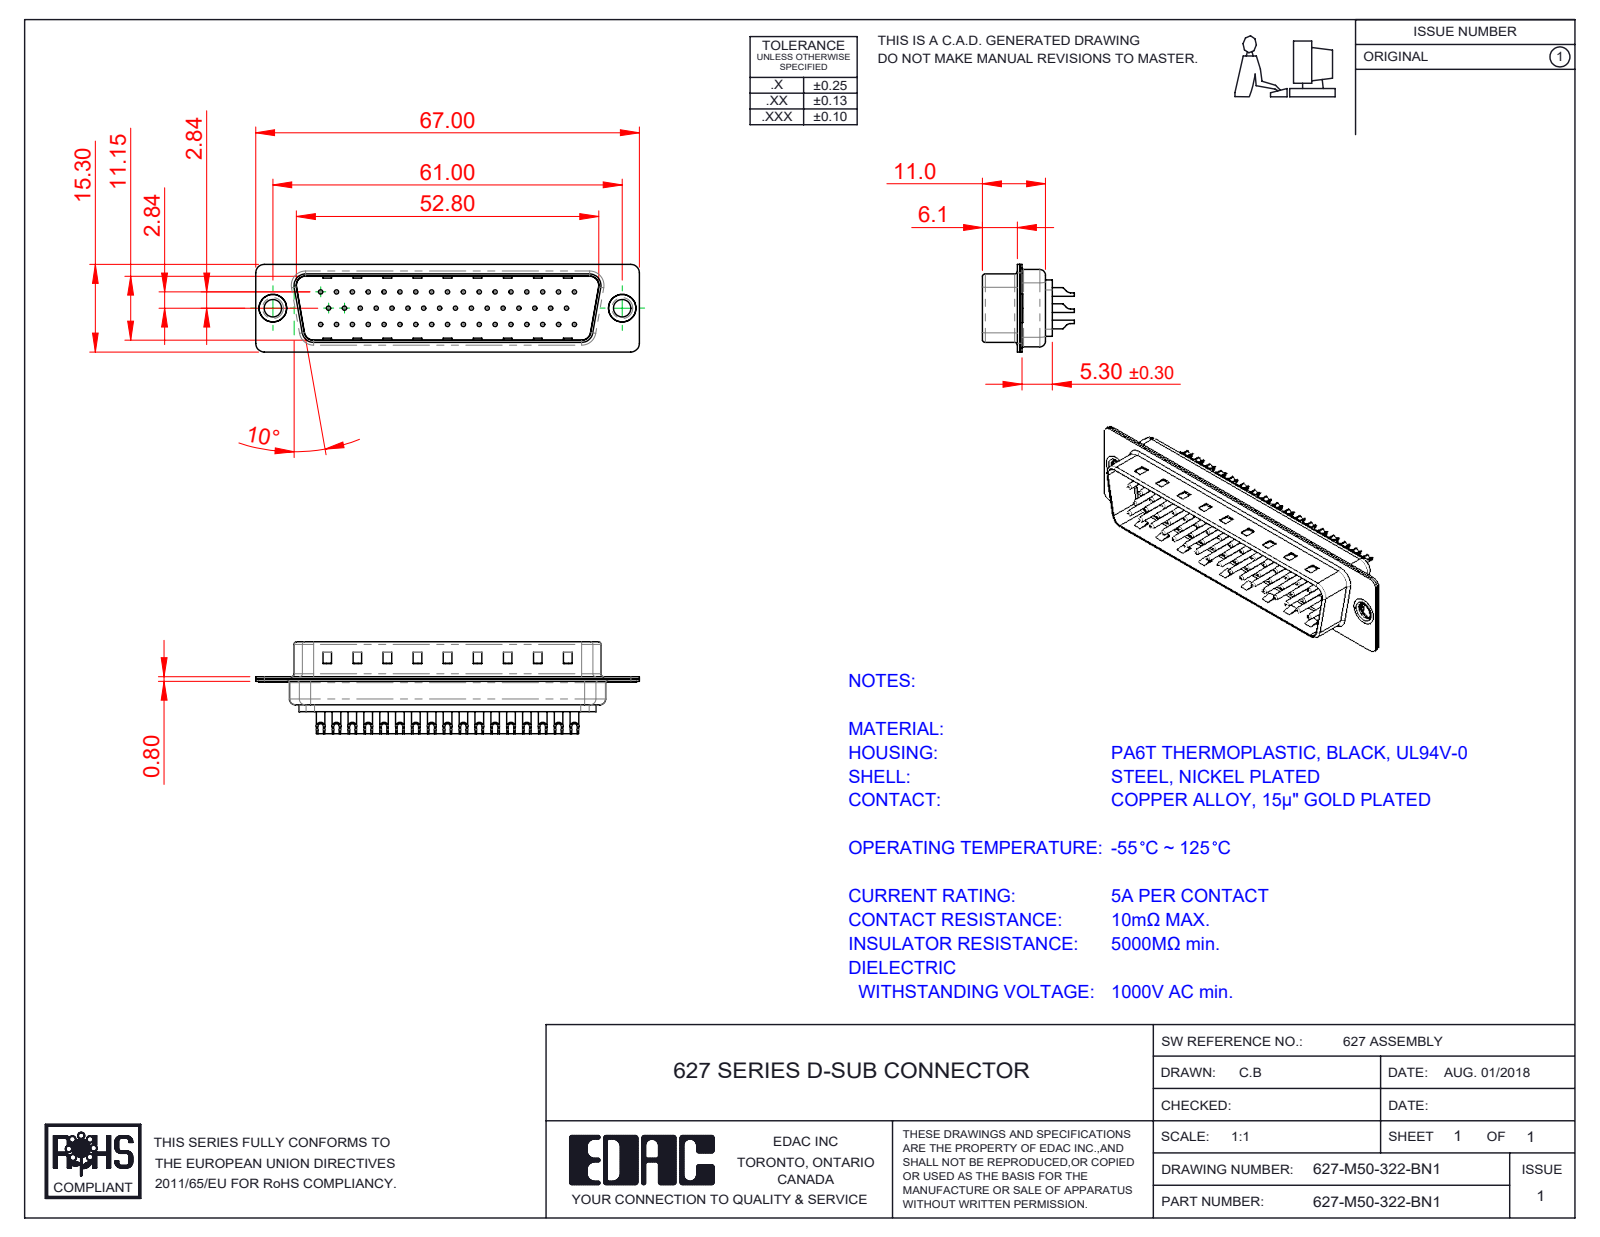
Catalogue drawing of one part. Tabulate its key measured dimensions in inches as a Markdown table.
| quantity | value |
| --- | --- |
| part name | 627M Contact Row 1_22; 627M Shell Front_50 Contacts; 627-M50-322-BN1; 627M Contact Row 2_22L (+4 more) |
| STEP written by | SolidWorks 2020 (CONFIG_CONTROL_DESIGN) |
| units | inches |
| bodies | 55 solids, 2236 faces (653 planar, 925 cylindrical, 658 other) |
| overall size | 2.638 × 0.632 × 0.602 |
| volume | 0.278 in³ |
| surface area | 17.08 in² |
| round holes (diameter × count) | 0.03 × 50, 0.039 × 50, 0.063 × 50, 0.079 × 50, 0.12 × 2, 0.157 × 2, 0.189 × 2 |
| round bosses / shafts (diameter × count) | 0.059 × 50, 0.197 × 2, 0.193 × 2, 0.14 × 2 |
| partial cylindrical surfaces (radius × count) | 0.059 × 16, 0.079 × 12, 0.02 × 8, 0.063 × 8, 0.039 × 7, 0.01 × 4, 0.024 × 4, 0.026 × 4 |
| main face-to-face distances | 0.016, 0.455, 0.224, 0.24, 0.031, 0.03, 0.485, 0.485, 0.516, 0.209 |
| hole center spacings | 0.124, 0.109, 0.218, 0.327, 0.436, 0.545, 0.654, 0.198 |
